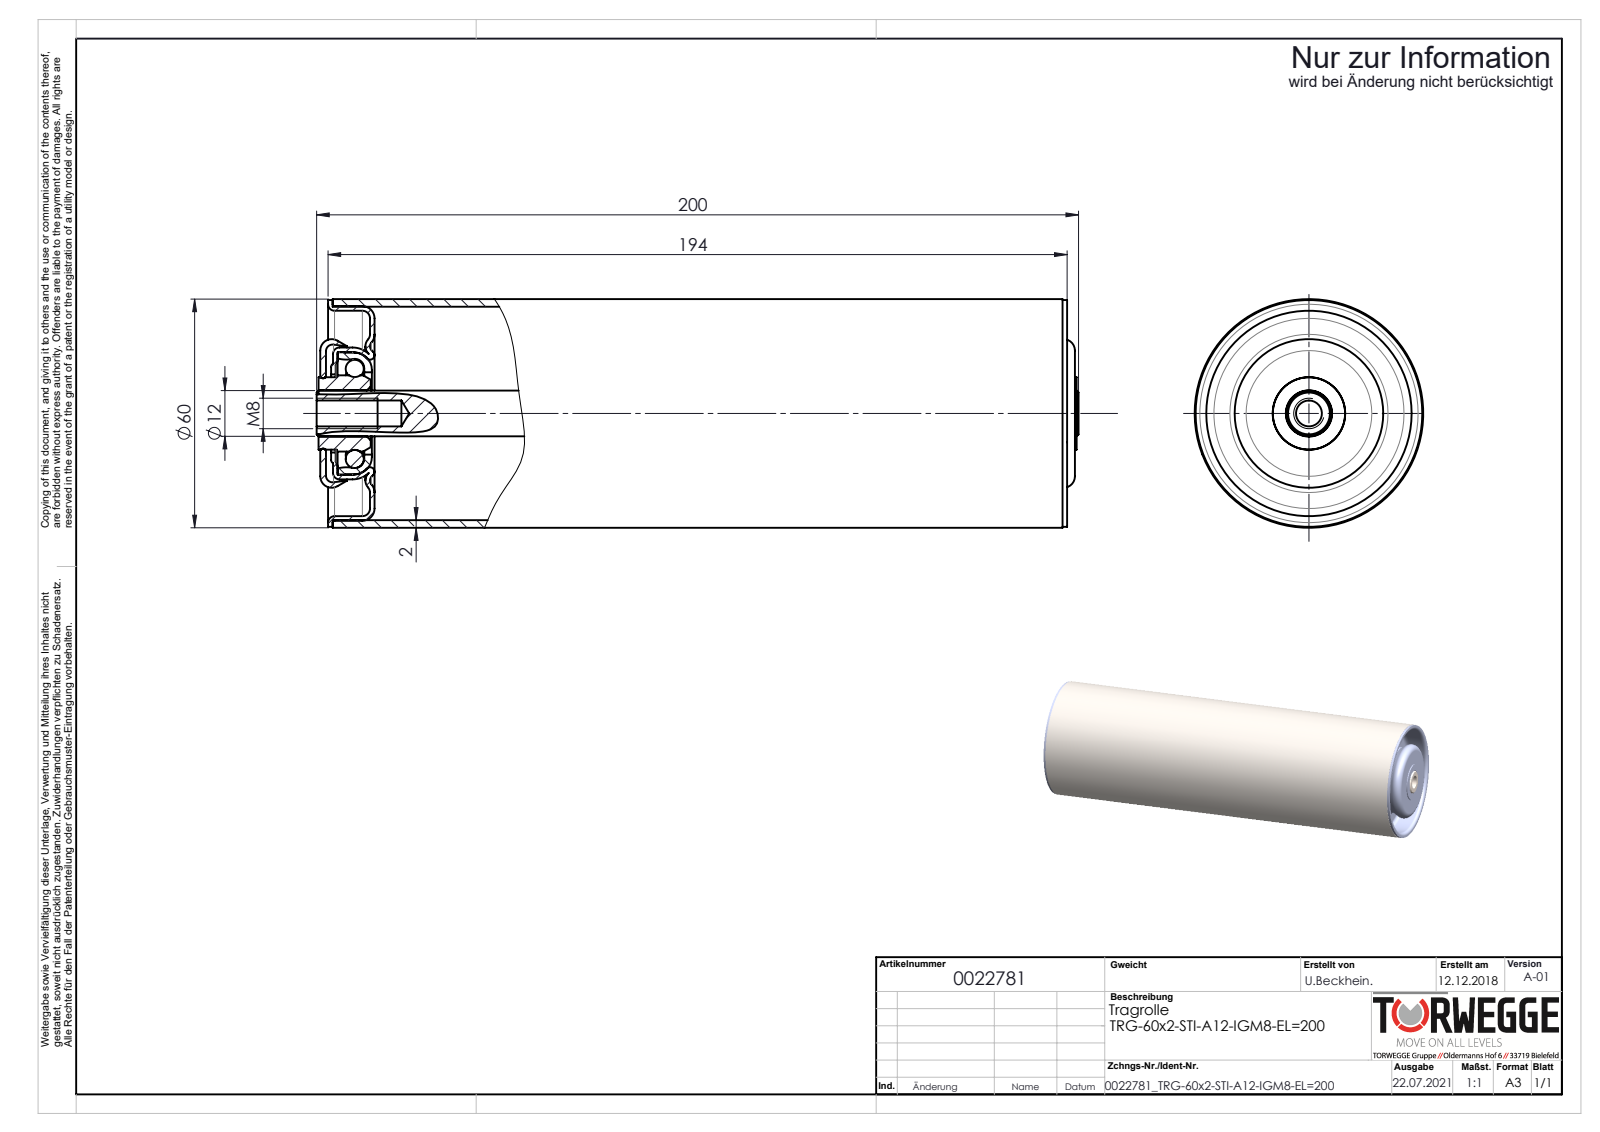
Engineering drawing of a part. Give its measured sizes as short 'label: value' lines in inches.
name: 0022781
written by: SolidWorks 2020 (AUTOMOTIVE_DESIGN)
unit: in
bodies: 40 solids, 318 faces (40 planar, 74 cylindrical, 204 other)
size: 7.874 × 2.362 × 2.362
volume: 7.154 in³; area: 181.5 in²
holes: 1× ⌀0.268, 1× ⌀0.478, 1× ⌀0.75, 1× ⌀0.807, 1× ⌀0.85, 1× ⌀1.268, 1× ⌀2.122, 1× ⌀2.205
bosses: 1× ⌀2.362, 1× ⌀2.343, 1× ⌀2.217, 1× ⌀1.362, 1× ⌀1.264, 1× ⌀1.256, 1× ⌀0.787, 1× ⌀0.748
face distances: 0.047, 0.433, 7.157, 6.724, 0.514, 0.561, 7.238, 7.285, 0.128, 7.671
